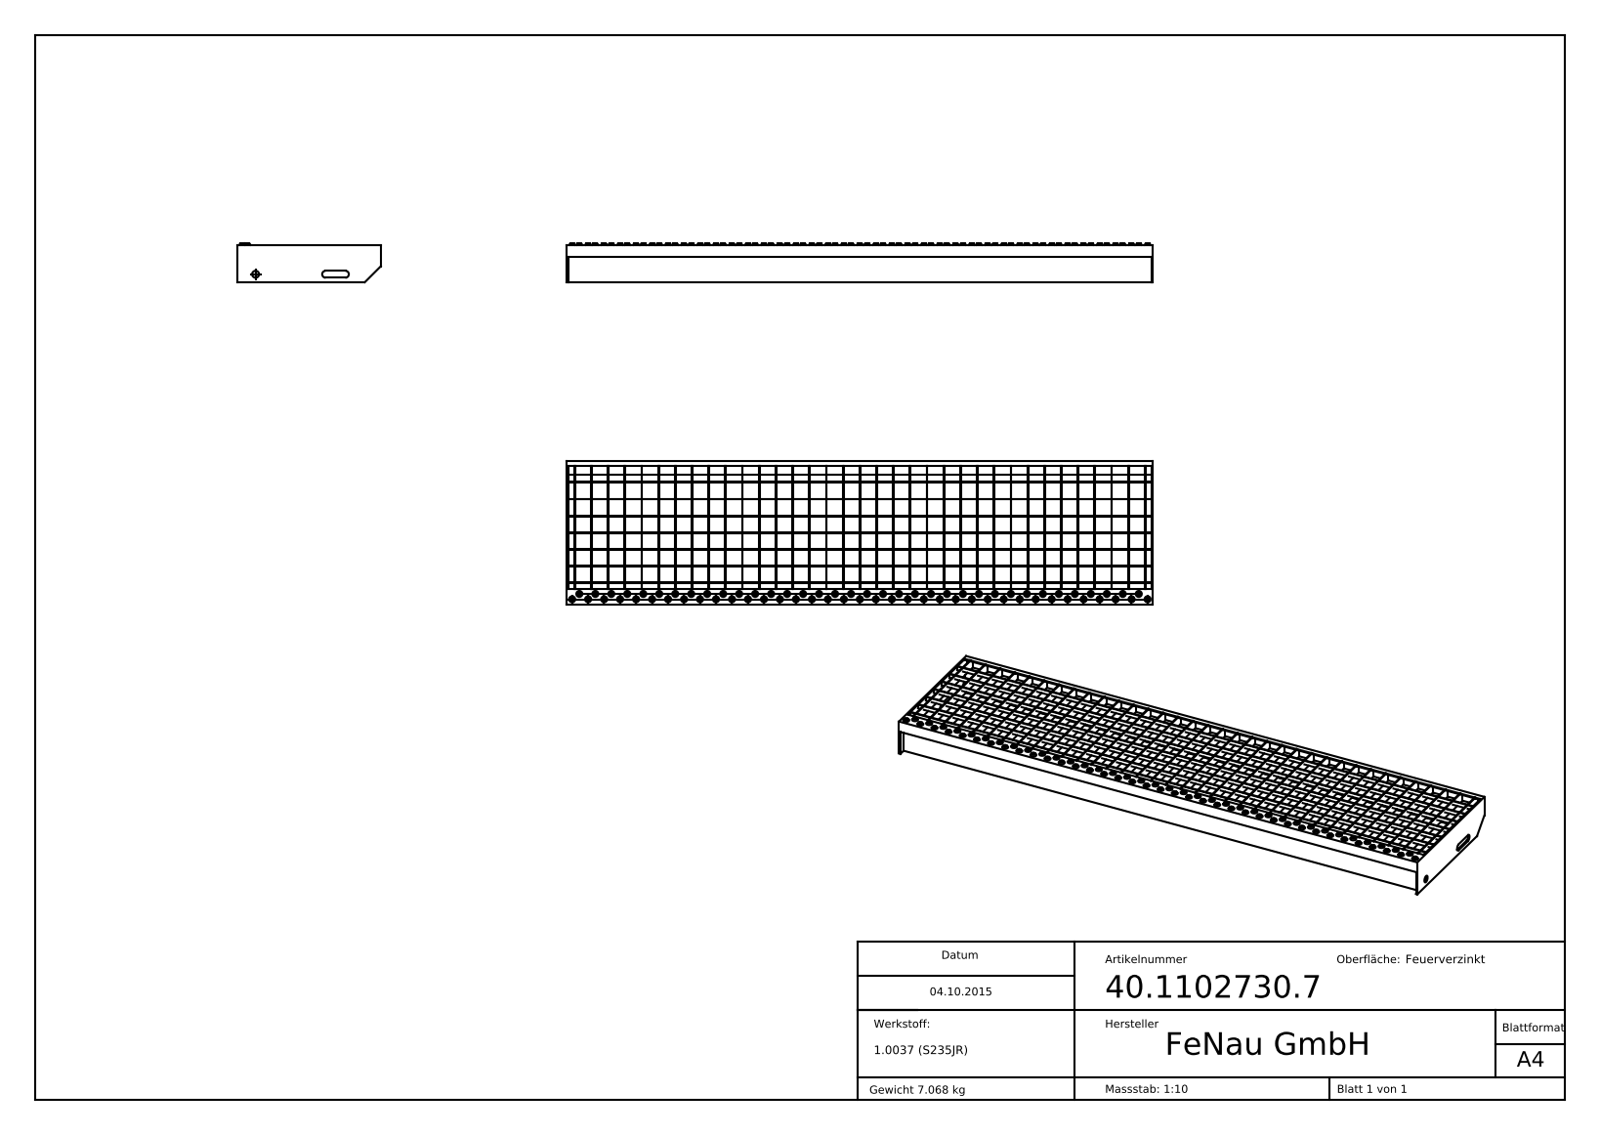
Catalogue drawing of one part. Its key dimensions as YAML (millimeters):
part_name: "40.1102730.7"
step_written_by: "SolidWorks 2015 (CONFIG_CONTROL_DESIGN)"
units: millimeters
bodies: {solids: 34, faces: 997, planar: 615, cylindrical: 156, other: 226}
overall_size: [1100, 270, 72.67]
volume: 906177
surface_area: 1061000
round_holes:
  - {diameter: 7, count: 73}
  - {diameter: 13, count: 1}
partial_cylinders:
  - {radius: 6.5, count: 2}
face_to_face_distances: [2, 31.5, 63, 94.5, 1.5, 33, 30, 126, 61.5, 64.5]
hole_center_spacings: [30, 60, 90, 120, 150, 180, 210, 240]
